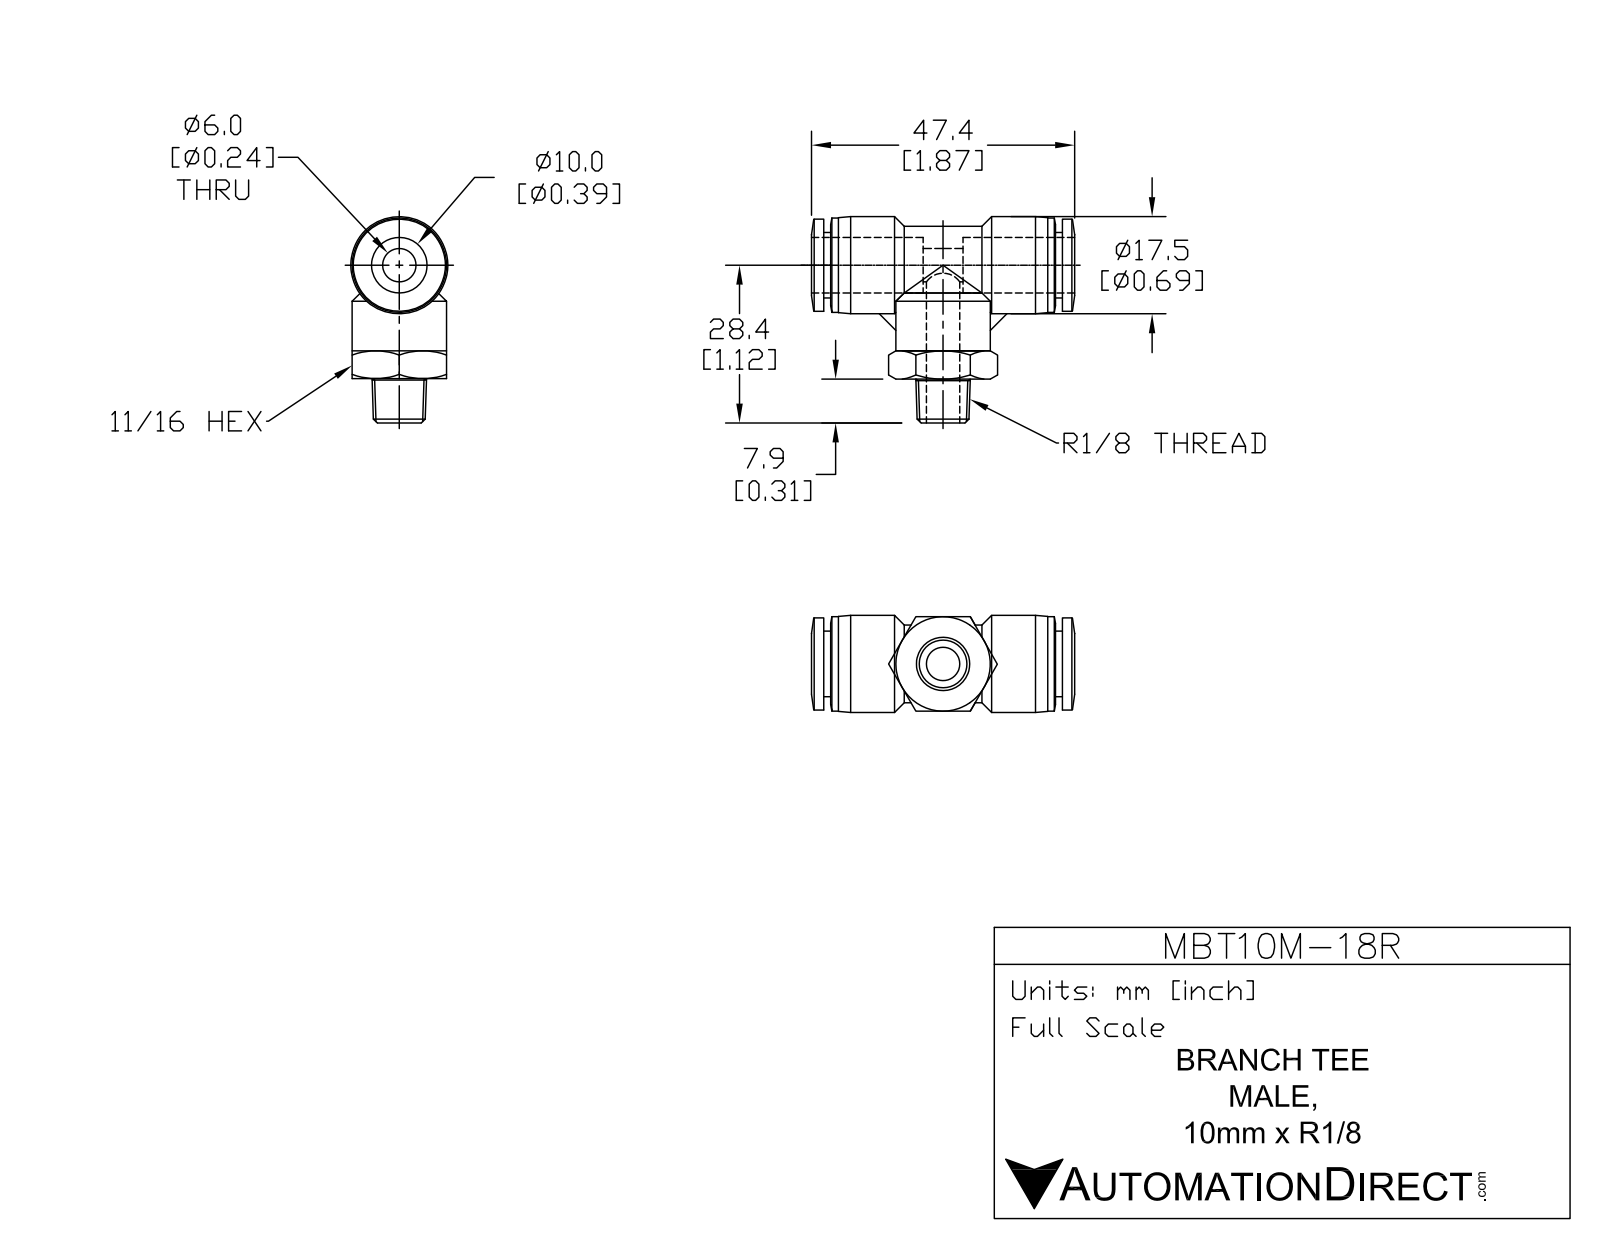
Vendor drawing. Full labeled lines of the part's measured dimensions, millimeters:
Part name (STEP PRODUCT): MBT10M-18R
STEP written by: SolidWorks 2015 (AUTOMOTIVE_DESIGN)
Units: millimetres
Bodies: 1 solid, 105 faces (24 planar, 34 cylindrical, 47 other)
Overall size (bounding box): 50.3 × 37.3 × 17.5
Volume: 9 670 mm³ · Surface area: 6 413 mm²
Round holes (diameter × count): ⌀6 ×2, ⌀10.3 ×1
Round bosses / shafts (diameter × count): ⌀17 ×2, ⌀17.5 ×1, ⌀16.6 ×1, ⌀14 ×1, ⌀11.8 ×1
Partial cylindrical surfaces — rounded edges, fillets, slot ends (radius × count): R7 ×1
Main face-to-face distances: 17, 1.2, 44.7, 18, 27.9, 16.7, 26.6, 45.9, 43.4, 9.9
